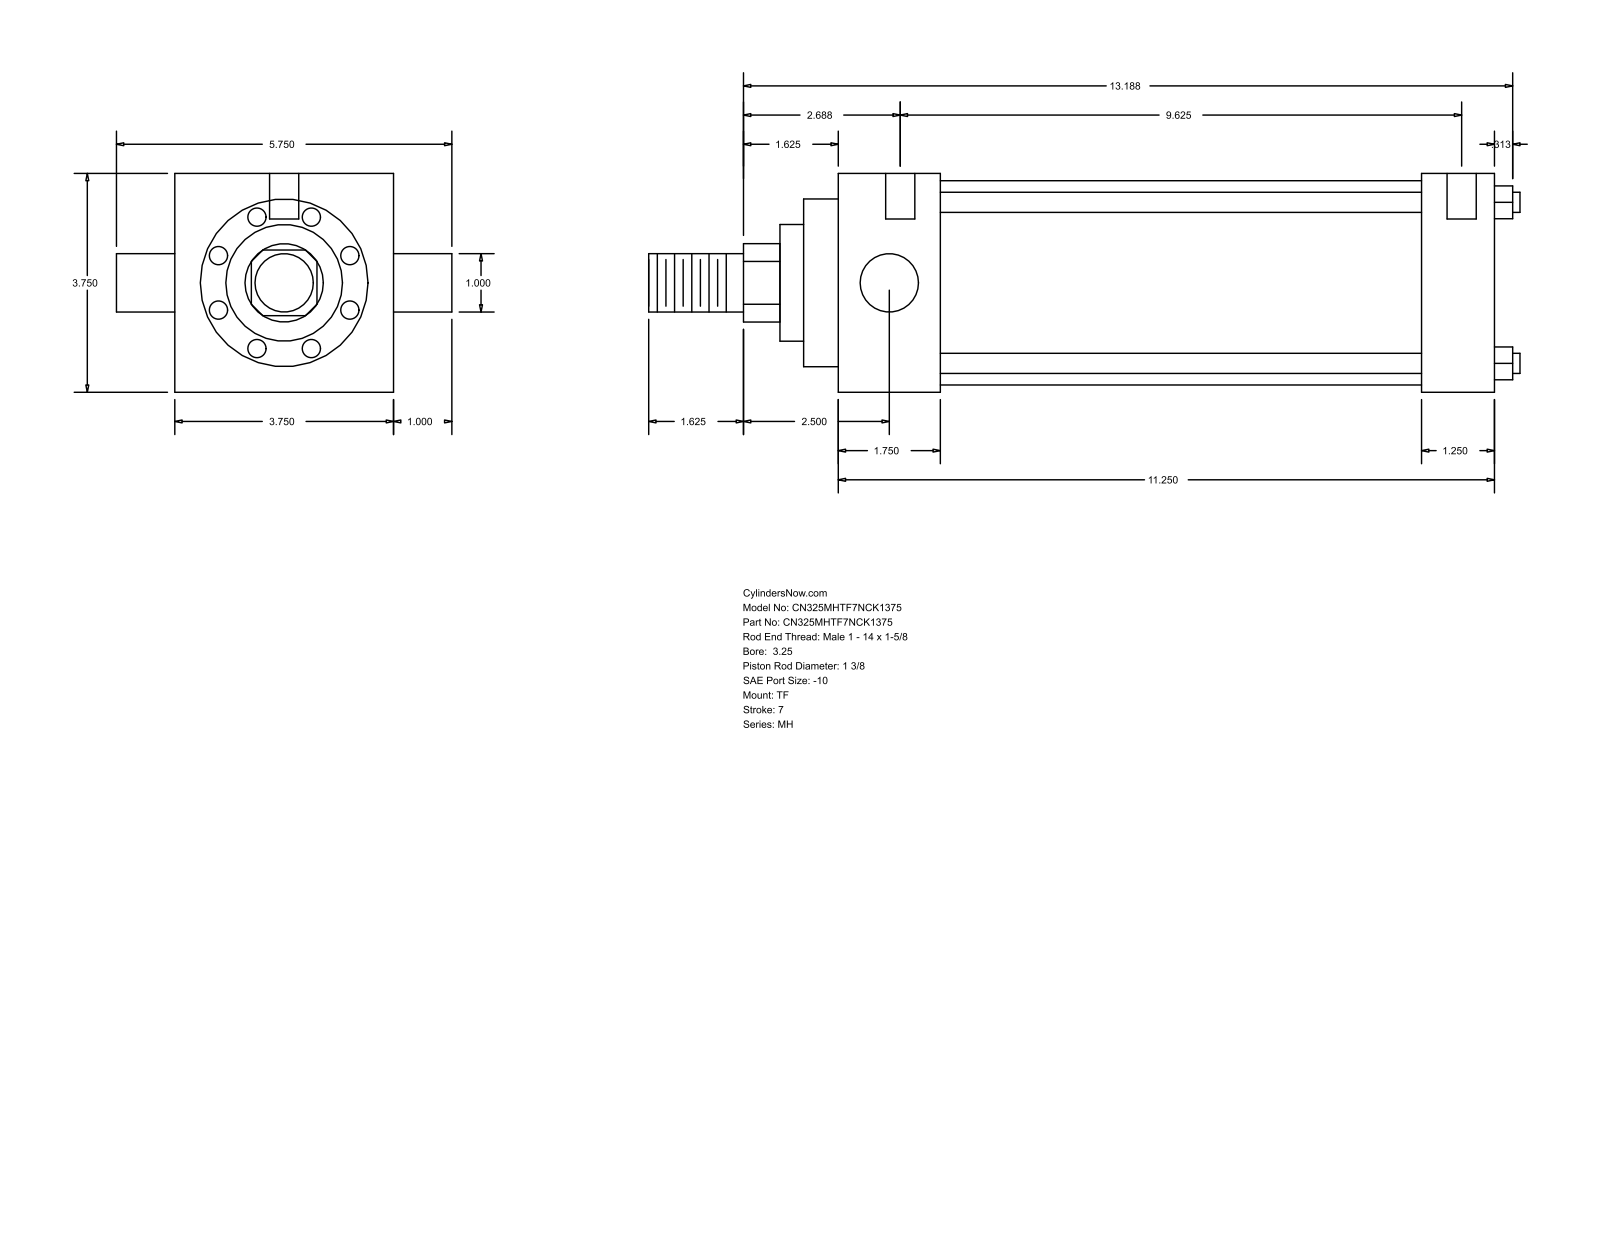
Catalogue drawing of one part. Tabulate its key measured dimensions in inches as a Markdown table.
| quantity | value |
| --- | --- |
| part name | MH_TF__0325_1.375 |
| STEP written by | GSSL Pune (CONFIG_CONTROL_DESIGN) |
| units | inches |
| bodies | 0 solids, 86 faces (61 planar, 25 cylindrical, 0 other) |
| overall size | 14.937 × 5.75 × 3.75 |
| round holes (diameter × count) | 0.219 × 3, 0.5 × 2 |
| round bosses / shafts (diameter × count) | 0.345 × 4, 1 × 2, 3.5 × 1, 2.875 × 1, 2 × 1, 1.375 × 1 |
| partial cylindrical surfaces (radius × count) | 0.672 × 1 |
| main face-to-face distances | 3.75, 11.25, 1.75, 10, 8.25, 9.5, 1.25, 0.594, 2.344, 10.594 |
| hole center spacings | 0.063, 0.187, 9.625, 9.688, 9.813, 9.875 |
